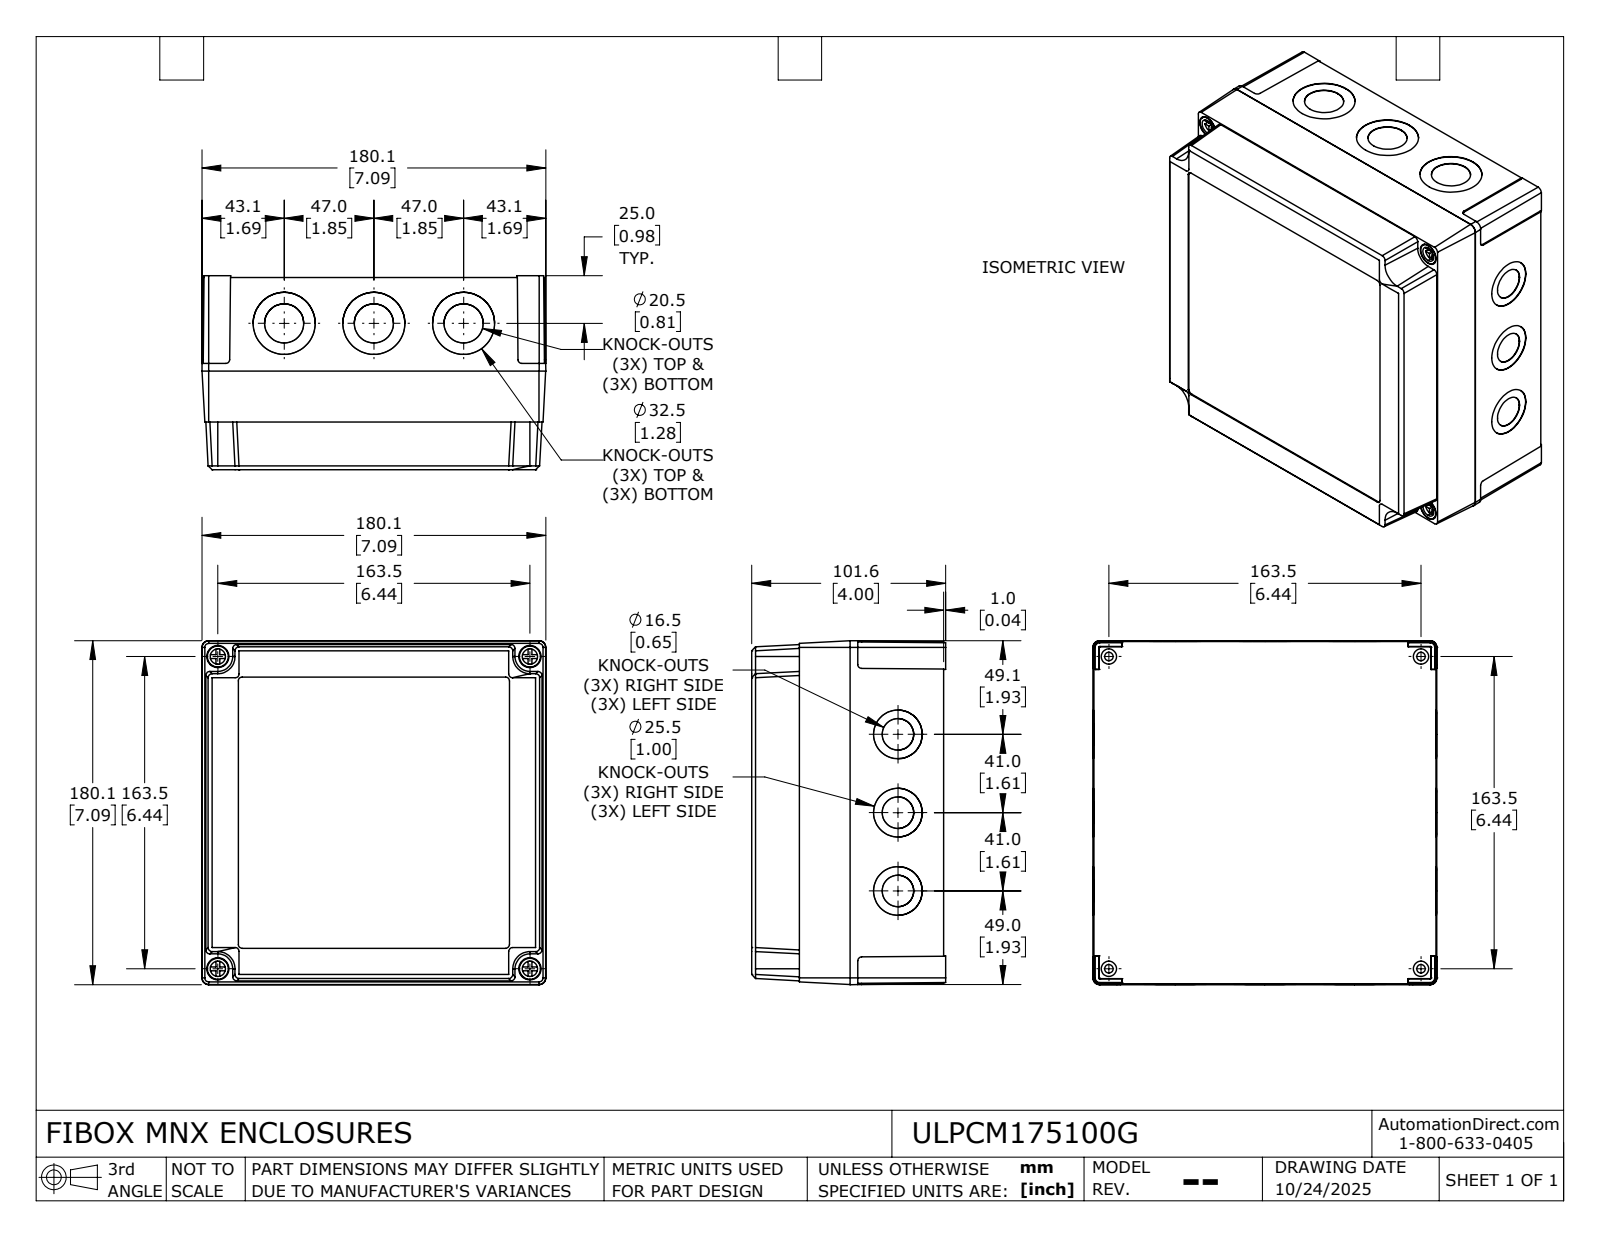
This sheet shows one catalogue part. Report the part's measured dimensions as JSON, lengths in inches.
{"part_name": "ULPCM175100G_Default", "step_written_by": "SolidWorks 2024 (CONFIG_CONTROL_DESIGN)", "units": "inches", "bodies": {"solids": 6, "faces": 629, "planar": 351, "cylindrical": 232, "other": 46}, "overall_size": [7.091, 7.091, 4], "volume_in3": 25.17, "surface_area_in2": 430.7, "round_holes": [[0.126, 12], [0.157, 12], [0.65, 6], [0.807, 6], [1.004, 6], [1.28, 6], [0.177, 4], [0.315, 4], [0.457, 4]], "round_bosses_or_shafts": [[0.315, 12], [0.098, 8], [0.433, 4], [0.283, 4]], "partial_cylinders_radius": [[0.079, 8], [0.083, 8], [0.112, 6], [0.042, 4], [0.197, 4], [0.046, 2]], "face_to_face_distances": [3.85, 0.118, 3.732, 0.165, 0.091, 3.941, 3.823, 0.077, 0.055, 0.022], "hole_center_spacings": [1.333, 1.969, 2.866, 3.252, 4.79, 5.207, 5.469, 5.853]}
